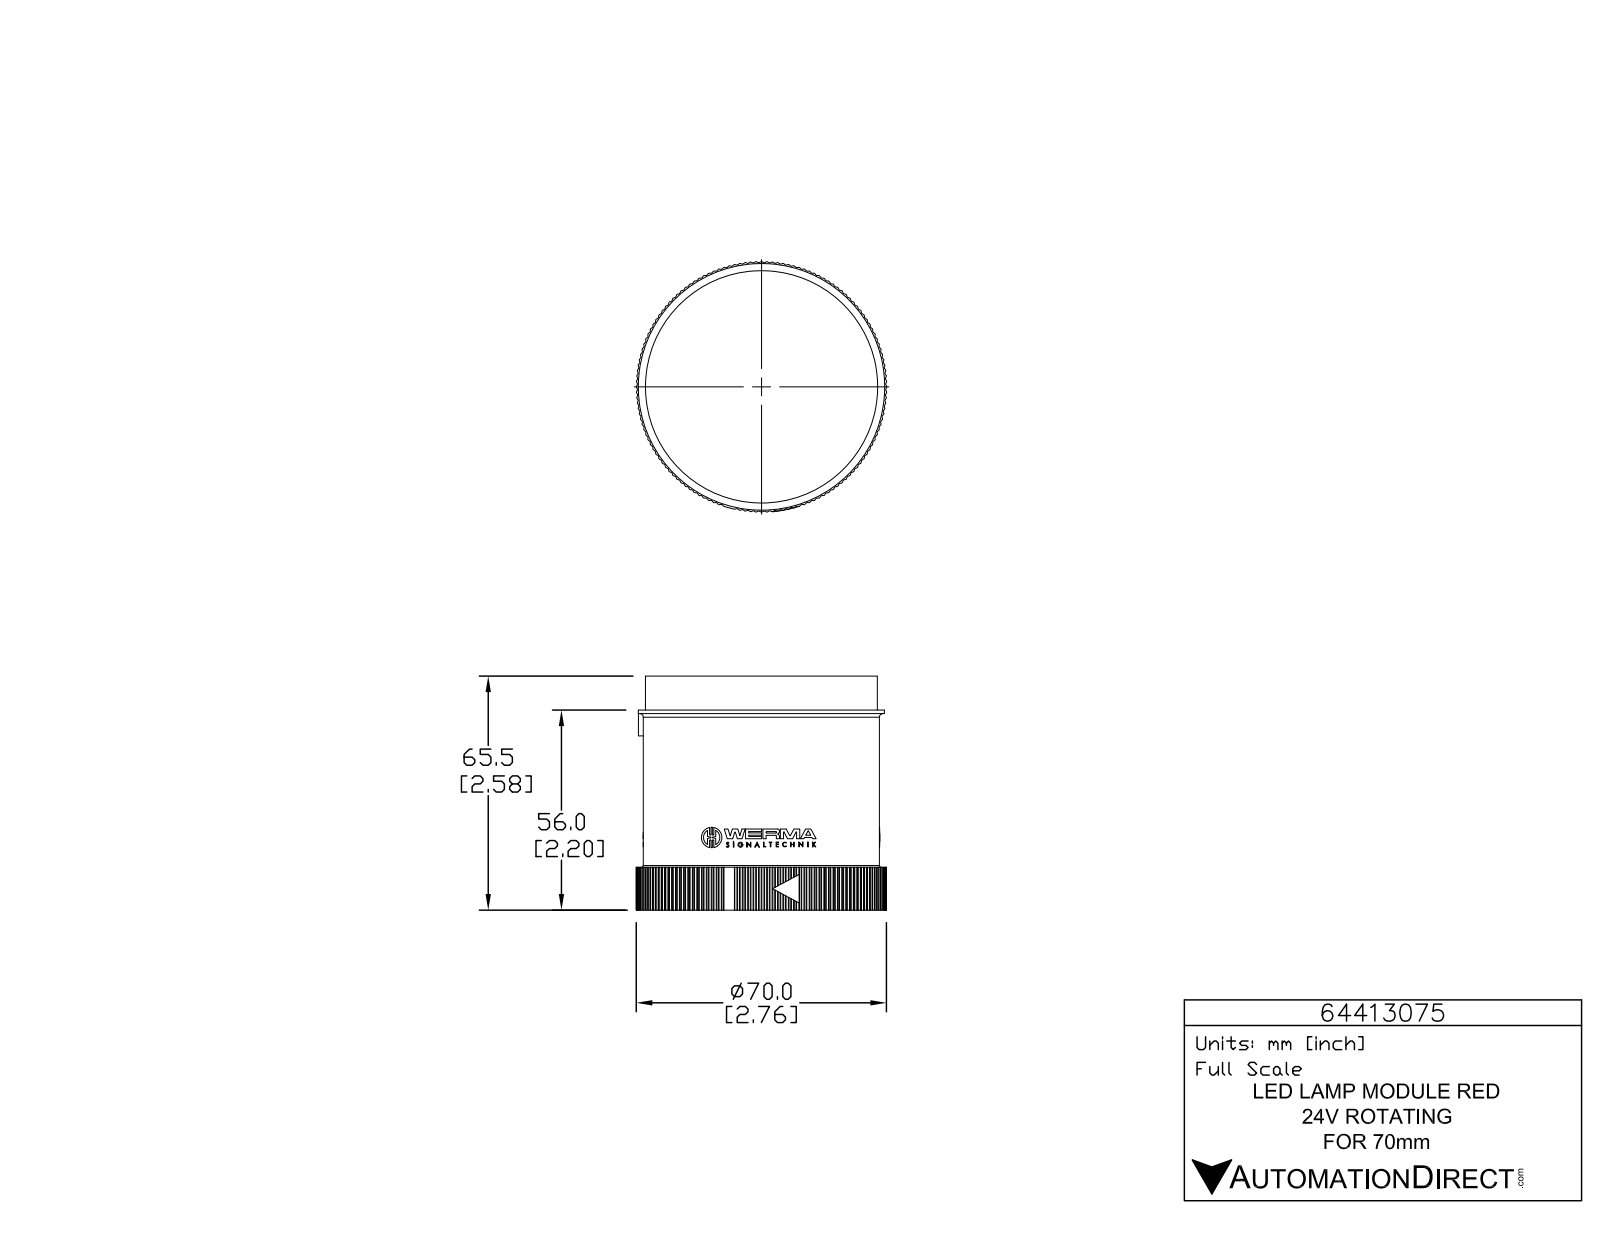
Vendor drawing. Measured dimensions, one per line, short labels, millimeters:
name: 64413075
written by: SolidWorks 2015 (AUTOMOTIVE_DESIGN)
unit: mm
bodies: 1 solid, 1400 faces (832 planar, 563 cylindrical, 5 other)
size: 70.2 × 70.2 × 65.5
volume: 197 000 mm³; area: 24 180 mm²
holes: 3× ⌀1, 1× ⌀65.4
bosses: 3× ⌀5.7, 3× ⌀1.4, 1× ⌀69, 1× ⌀66.2, 1× ⌀65
rounds: 285× R0.2, 6× R0.2, 6× R0.2, 6× R0.2, 6× R3.3, 3× R0.1, 3× R0.1, 3× R0.2
face distances: 55.9, 62.3, 9.6, 65.5, 56, 46.4, 9.5, 62.3, 12, 2.4
